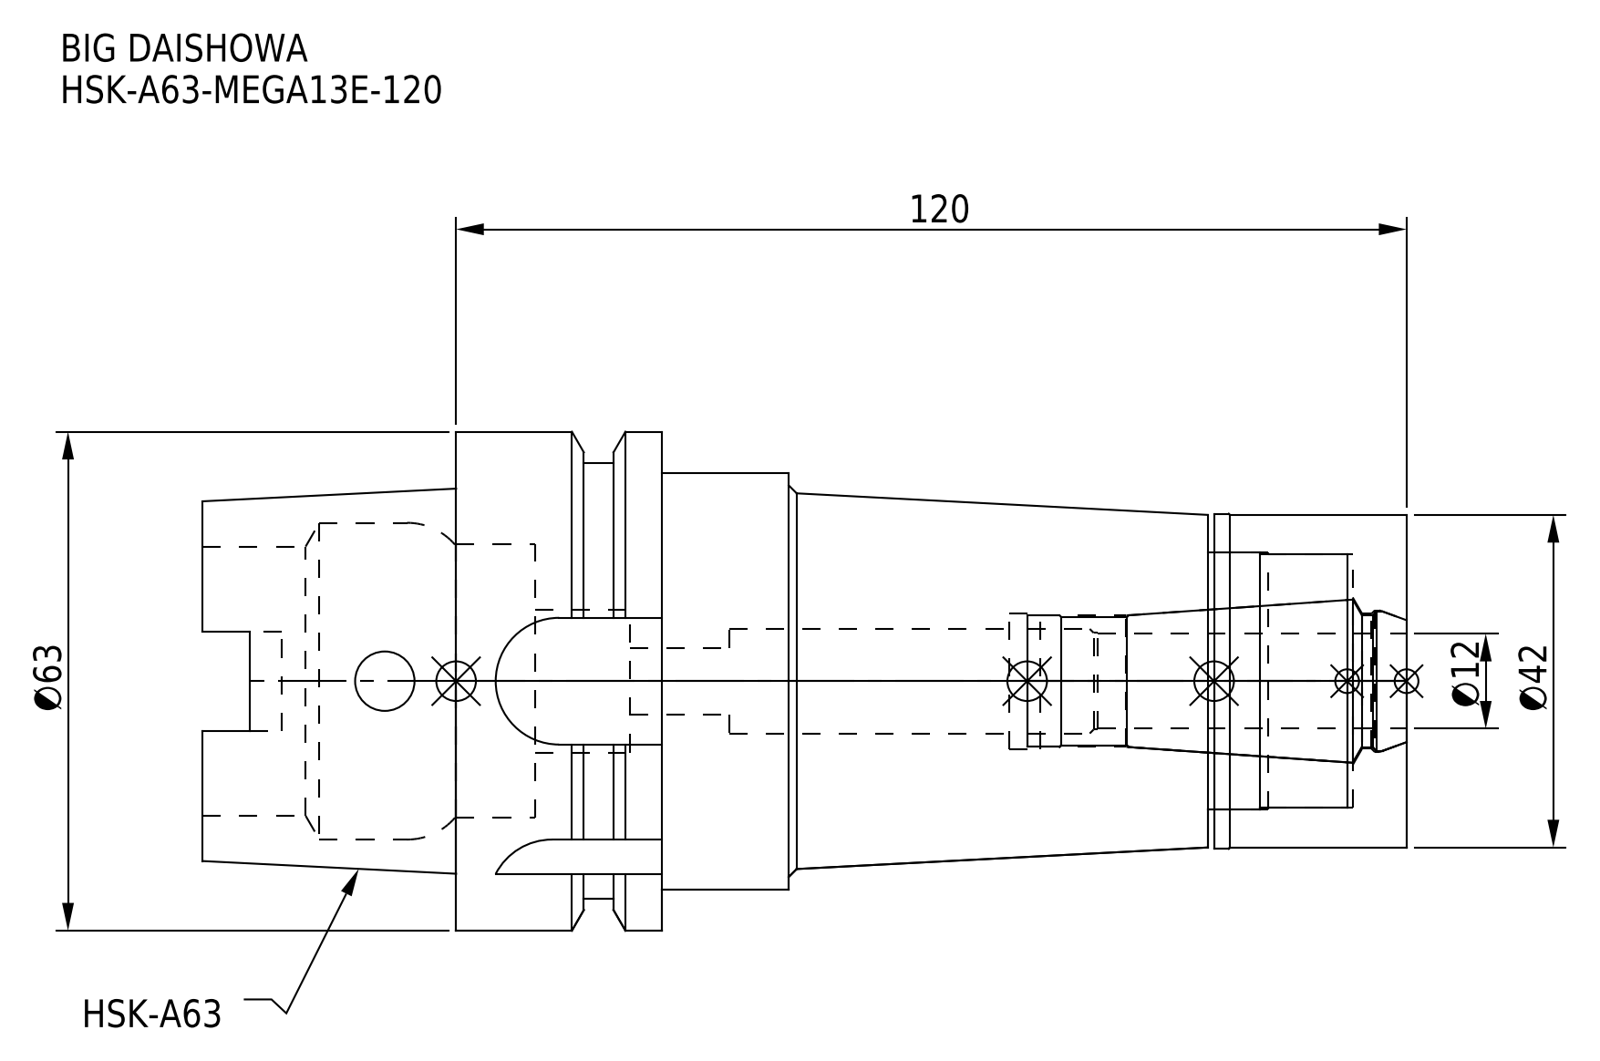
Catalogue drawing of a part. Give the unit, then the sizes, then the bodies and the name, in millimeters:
Units: millimetres
Overall size (bounding box): 152 × 63 × 63
Round holes (diameter × count): ⌀7.5 ×1, ⌀8.4 ×1, ⌀13.3 ×1, ⌀16.6 ×1, ⌀17 ×1, ⌀17.2 ×1, ⌀17.9 ×1, ⌀18 ×1, ⌀32 ×1, ⌀32.5 ×1, ⌀34 ×1, ⌀34.5 ×1
Round bosses / shafts (diameter × count): ⌀63 ×1, ⌀55 ×1, ⌀52.6 ×1, ⌀42.3 ×1, ⌀42 ×1
Partial cylindrical surfaces — rounded edges, fillets, slot ends (radius × count): R2.8 ×2, R2.88 ×2, R8 ×2, R9 ×1
Main face-to-face distances: 120, 26, 94, 110.05, 16.05, 9.95, 25.1, 24.3, 69.7, 85.75
Volume: 215 851 mm³ · Surface area: 45 452 mm²
Bodies: 2 solids, 127 faces (45 planar, 54 cylindrical, 28 other)
Part name (STEP PRODUCT): DXF_TEMP_ASSY_ASM_4_ASM.stp; HSK-A63-MEGA13E-120_1.stp; HSK-A63-MEGA13E-120-120-FreeParts; MEN13_1.stp (+3 more)
STEP written by: SolidWorks 2019 (CONFIG_CONTROL_DESIGN)
